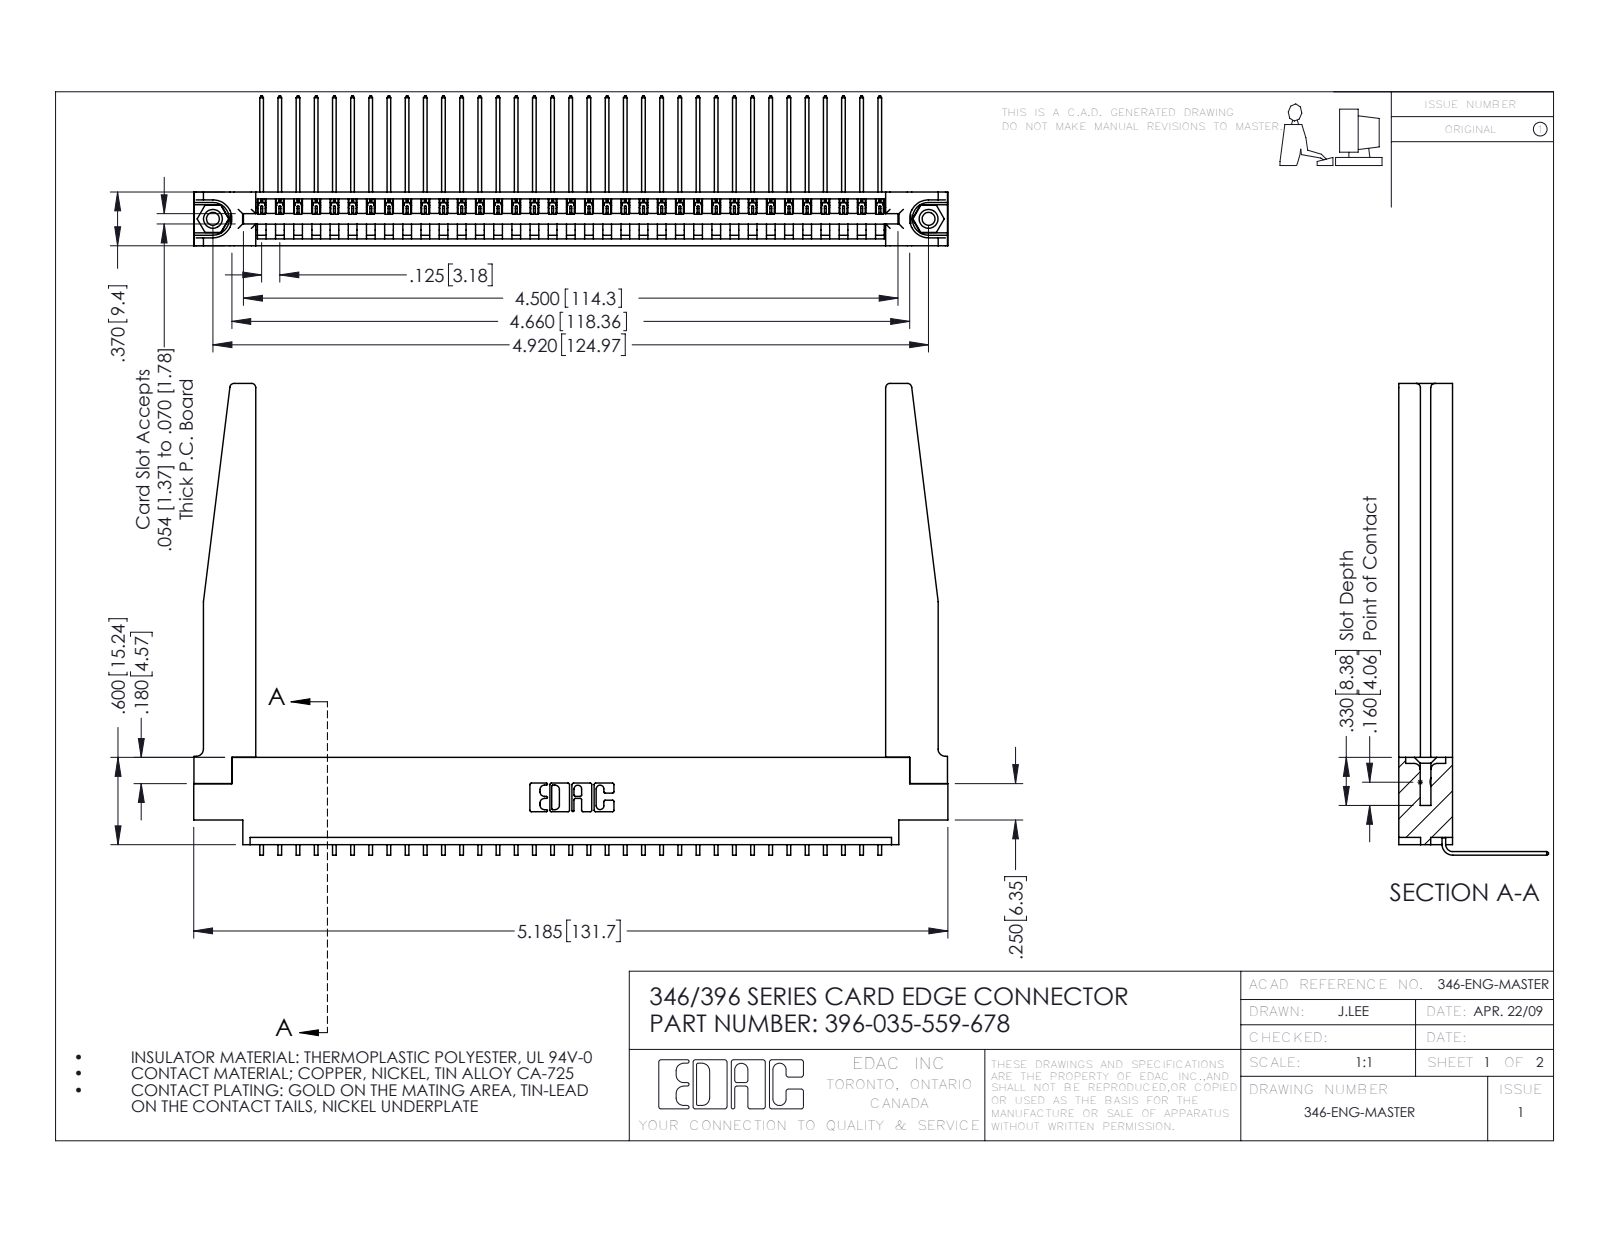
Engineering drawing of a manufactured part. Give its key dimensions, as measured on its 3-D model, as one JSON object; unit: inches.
{"part_name": "346-220-078_345-220-078; 346 Part_0.170 Offset - 0.156 Dia-TH; 345-292-001_558 559 Tail - 1; 345-250-001_345-250-001-102 (+1 more)", "step_written_by": "SolidWorks 2016 (CONFIG_CONTROL_DESIGN)", "units": "inches", "bodies": {"solids": 40, "faces": 2460, "planar": 1692, "cylindrical": 716, "other": 52}, "overall_size": [5.185, 3.243, 1.03], "volume_in3": 1.186, "surface_area_in2": 35.6, "round_holes": [[0.089, 2], [0.125, 2], [0.156, 2], [0.064, 1]], "round_bosses_or_shafts": [[0.155, 2]], "partial_cylinders_radius": [[0.006, 70], [0.01, 22], [0.03, 8], [0.007, 6], [0.031, 6], [0.026, 3], [0.05, 3], [0.031, 2]], "face_to_face_distances": [0.37, 0.048, 0.322, 0.072, 0.148, 0.15, 0.025, 0.25, 0.298, 0.222], "hole_center_spacings": [0.246, 4.711, 4.92]}
